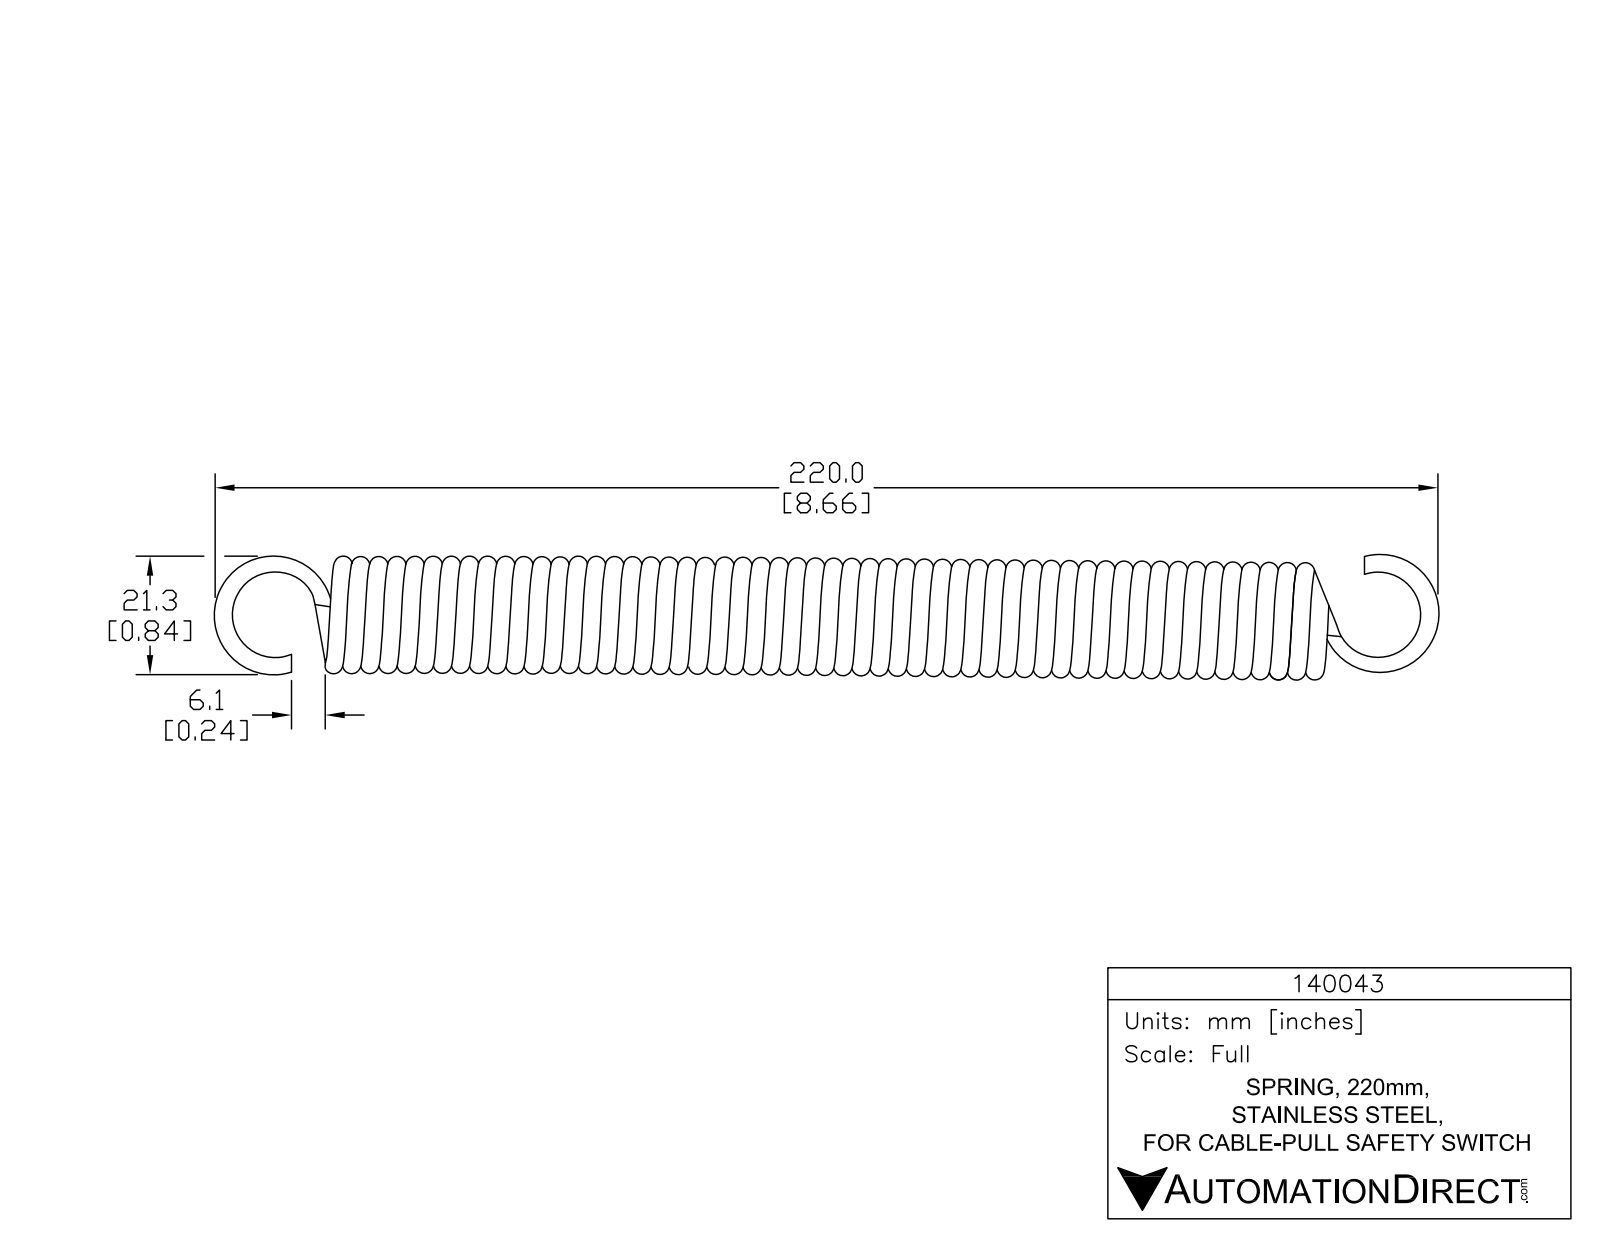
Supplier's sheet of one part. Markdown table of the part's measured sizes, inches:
| quantity | value |
| --- | --- |
| part name | 140043 |
| STEP written by | SolidWorks 2017 (AUTOMOTIVE_DESIGN) |
| units | inches |
| bodies | 1 solid, 18 faces (8 planar, 0 cylindrical, 10 other) |
| overall size | 8.674 × 0.847 × 0.83 |
| volume | 1.557 in³ |
| surface area | 49.5 in² |
| main face-to-face distances | 7.617 |
